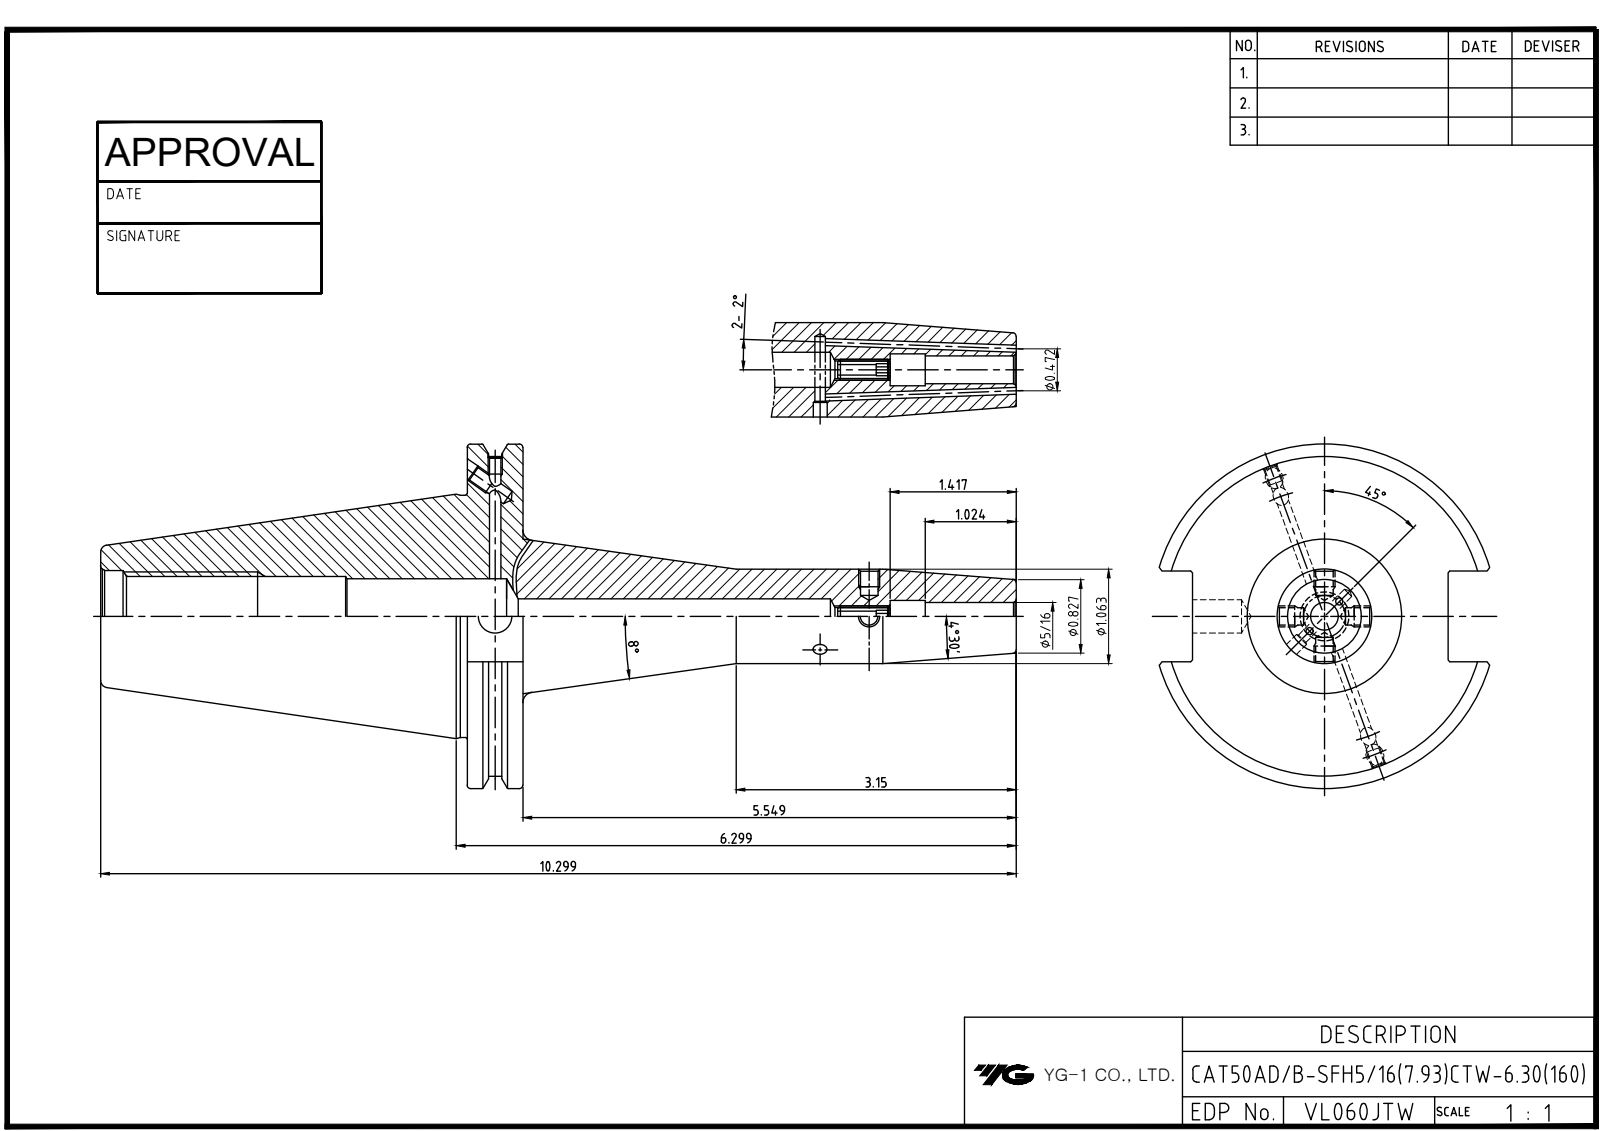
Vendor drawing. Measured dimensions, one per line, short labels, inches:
name: LO-CAT50ADB-SFH7.9375CTW-160
written by: Autodesk Inventor 2022 (AUTOMOTIVE_DESIGN)
unit: in
bodies: 1 solid, 93 faces (37 planar, 30 cylindrical, 26 other)
size: 10.299 × 3.875 × 3.728
volume: 25.22 in³; area: 95.43 in²
holes: 2× ⌀0.098, 2× ⌀0.128, 2× ⌀0.163, 2× ⌀0.165, 2× ⌀0.197, 1× ⌀0.194, 1× ⌀0.313, 1× ⌀0.36, 1× ⌀0.375, 1× ⌀0.394, 1× ⌀0.846, 1× ⌀0.865
bosses: 1× ⌀3.875, 1× ⌀3.594, 1× ⌀2.726, 1× ⌀1.063
face distances: 0.625, 4.125, 4.75, 2.875, 1.02, 10.299, 6.174, 5.549, 4.363, 0.238
